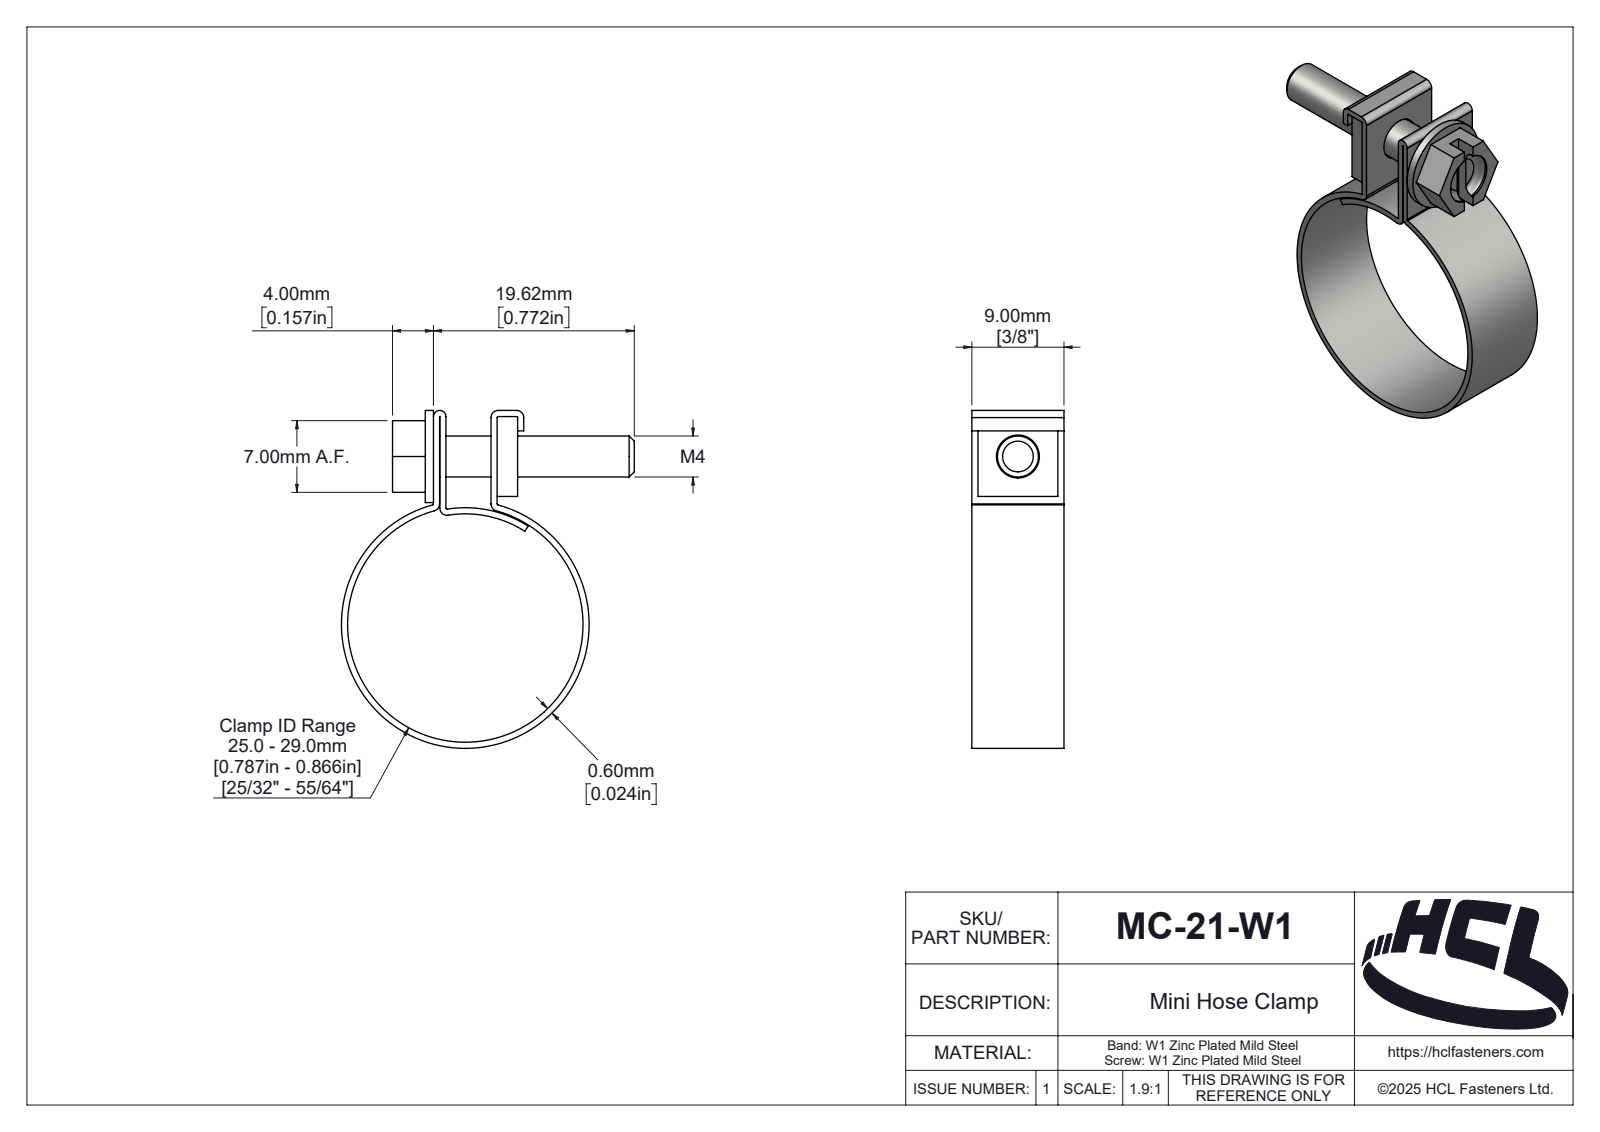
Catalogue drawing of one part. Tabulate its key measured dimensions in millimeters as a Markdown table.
| quantity | value |
| --- | --- |
| part name | MC-21-W1 |
| STEP written by | SolidWorks 2025 (AUTOMOTIVE_DESIGN) |
| units | millimeters |
| bodies | 3 solids, 175 faces (38 planar, 84 cylindrical, 53 other) |
| overall size | 33 × 28.61 × 9 |
| volume | 1 059 mm³ |
| surface area | 2 720 mm² |
| round holes (diameter × count) | 4.2 × 1, 5 × 1, 23 × 1 |
| round bosses / shafts (diameter × count) | 24.2 × 1, 9 × 1, 4 × 1 |
| partial cylindrical surfaces (radius × count) | 0.1 × 5, 0.7 × 5, 0.2 × 1, 0.61 × 1, 0.81 × 1, 1.01 × 1, 1.06 × 1, 1.28 × 1 |
| main face-to-face distances | 0.6, 0.62, 5, 5.62, 6.22, 7, 2, 2.6, 8.22, 7.6 |
